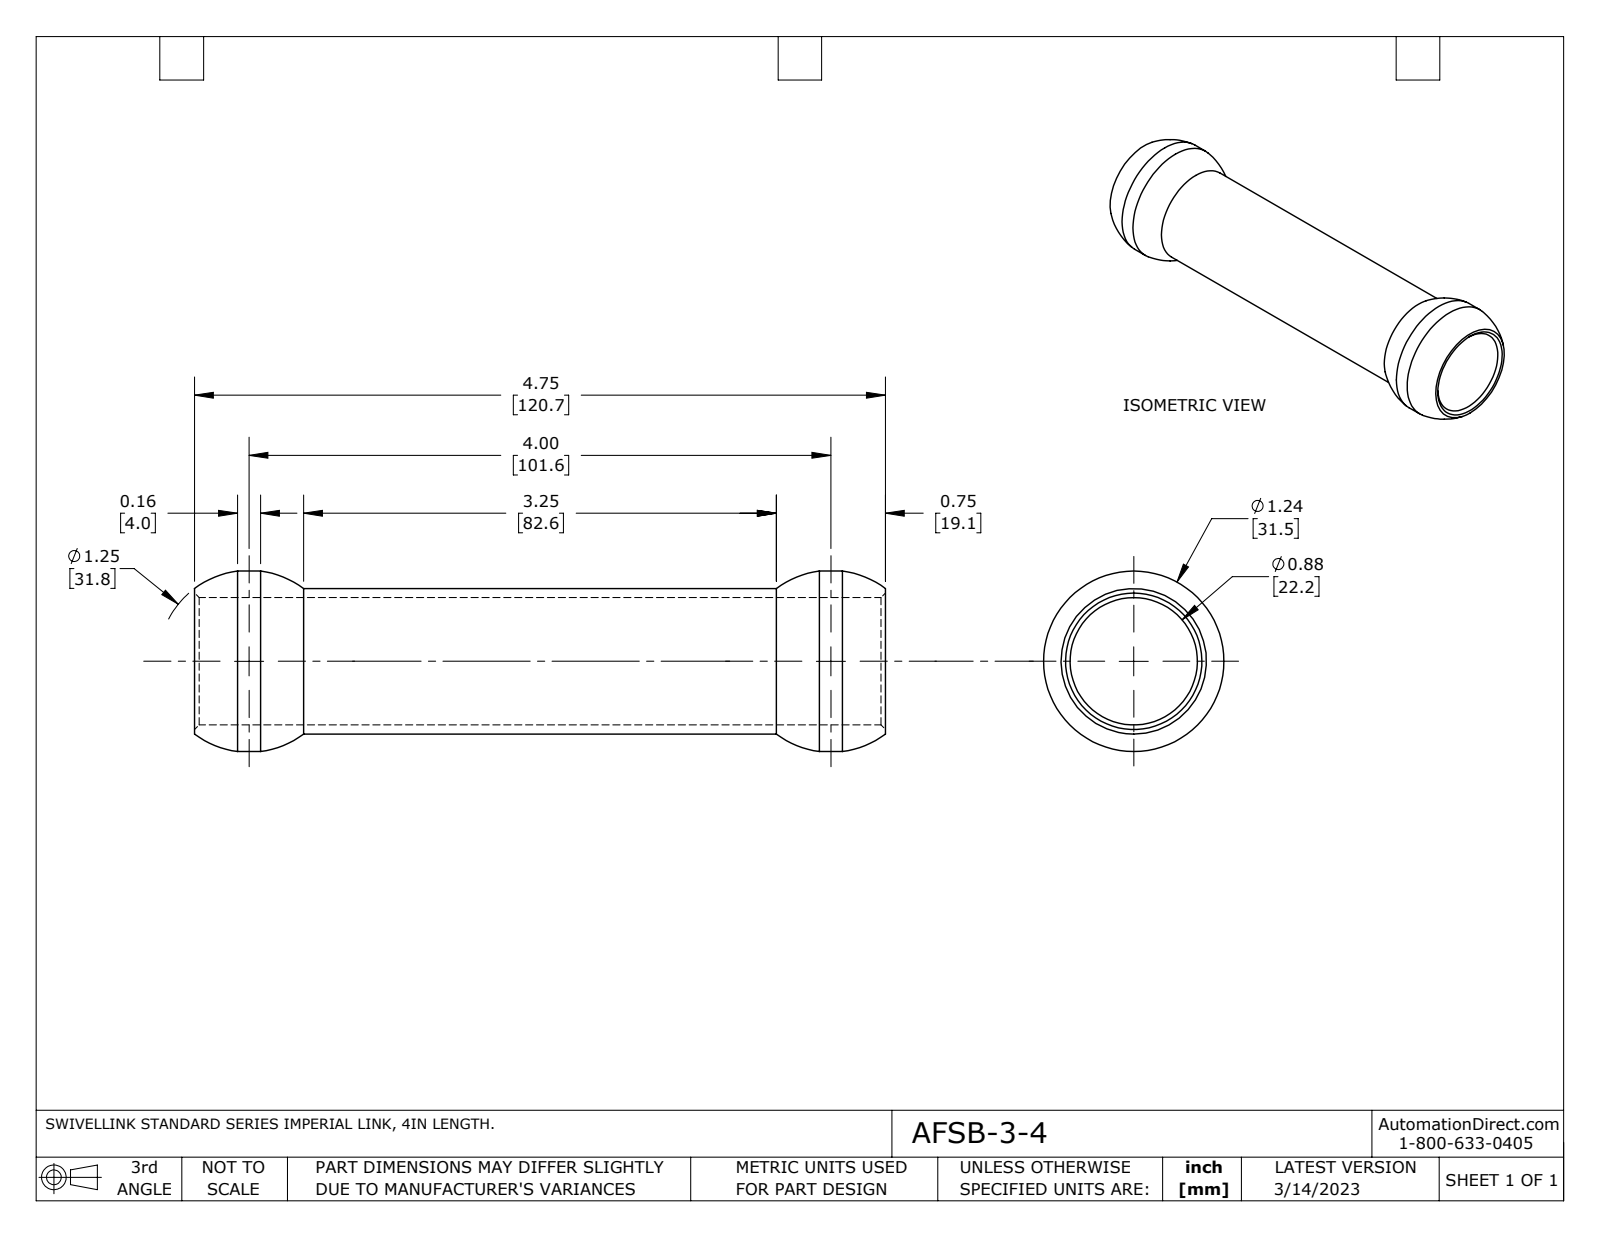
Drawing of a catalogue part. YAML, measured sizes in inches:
part_name: "AFSB-3-4"
step_written_by: "SolidWorks 2021 (AUTOMOTIVE_DESIGN)"
units: inches
bodies: {solids: 1, faces: 12, planar: 2, cylindrical: 4, other: 6}
overall_size: [4.75, 1.24, 1.24]
volume: 1.305
surface_area: 29.39
round_holes:
  - {diameter: 0.875, count: 1}
round_bosses_or_shafts:
  - {diameter: 1.24, count: 1}
  - {diameter: 1, count: 1}
face_to_face_distances: [4.75]
